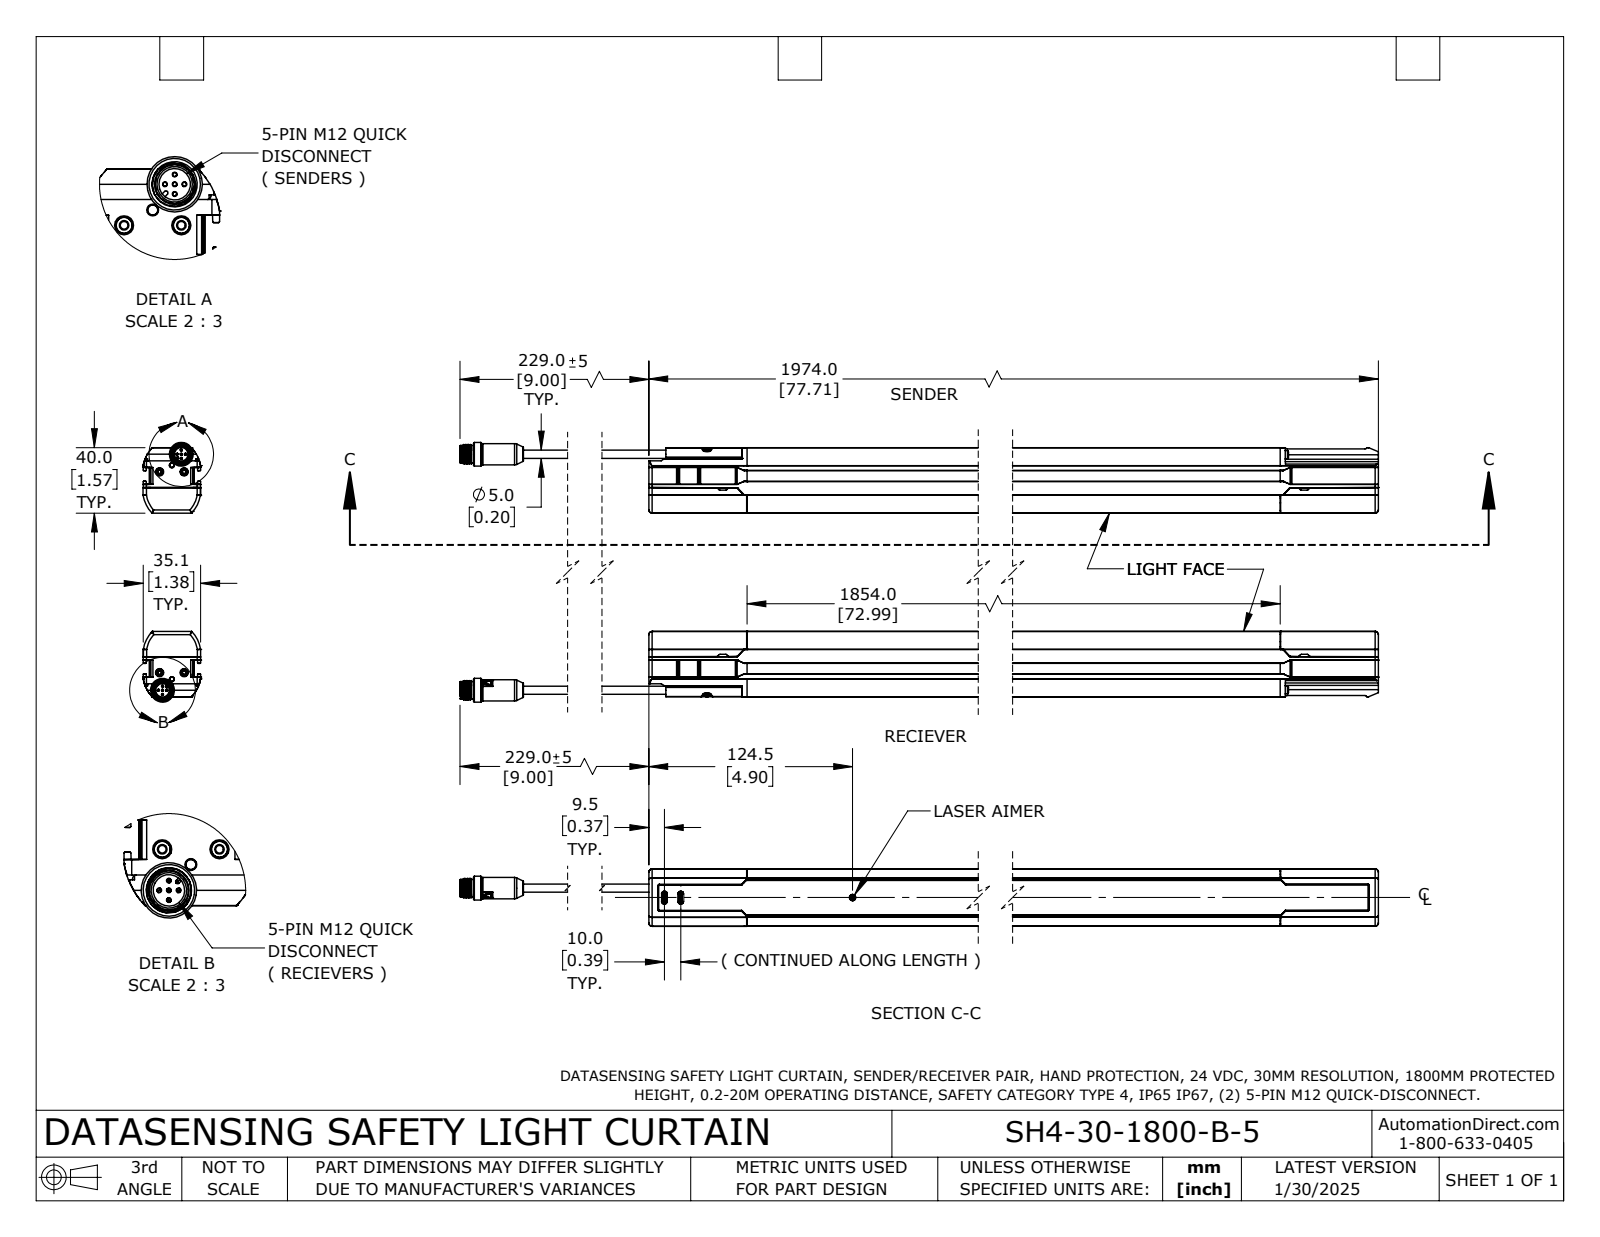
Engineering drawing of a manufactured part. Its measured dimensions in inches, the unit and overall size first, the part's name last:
Units: inches
Overall size (bounding box): 80.209 × 6.248 × 1.384
Round holes (diameter × count): ⌀0.079 ×4, ⌀0.1 ×4, ⌀0.118 ×4, ⌀0.197 ×4, ⌀0.1 ×2, ⌀0.101 ×2, ⌀0.11 ×2, ⌀0.325 ×2, ⌀0.382 ×2, ⌀0.407 ×2, ⌀0.425 ×2
Round bosses / shafts (diameter × count): ⌀0.197 ×10, ⌀0.039 ×10, ⌀0.087 ×8, ⌀0.172 ×4, ⌀0.571 ×2, ⌀0.512 ×2, ⌀0.417 ×2, ⌀0.374 ×2
Partial cylindrical surfaces — rounded edges, fillets, slot ends (radius × count): R0.01 ×164, R0.016 ×66, R0.02 ×50, R0.008 ×36, R0.031 ×20, R0.031 ×12, R0.079 ×12, R0.059 ×10
Main face-to-face distances: 1.496, 4.496, 0.156, 1.222, 3, 5.992, 1.378, 1.067, 4.634, 0.069
Hole centre spacings: 0.866, 5.057, 5.131, 0.429, 0.591, 0.672, 4.831, 4.867
Volume: 261.3 in³ · Surface area: 1 080 in²
Bodies: 4 solids, 2590 faces (1186 planar, 778 cylindrical, 626 other)
Part name (STEP PRODUCT): SH4-30-1800-B-5
STEP written by: SolidWorks 2024 (AUTOMOTIVE_DESIGN)
